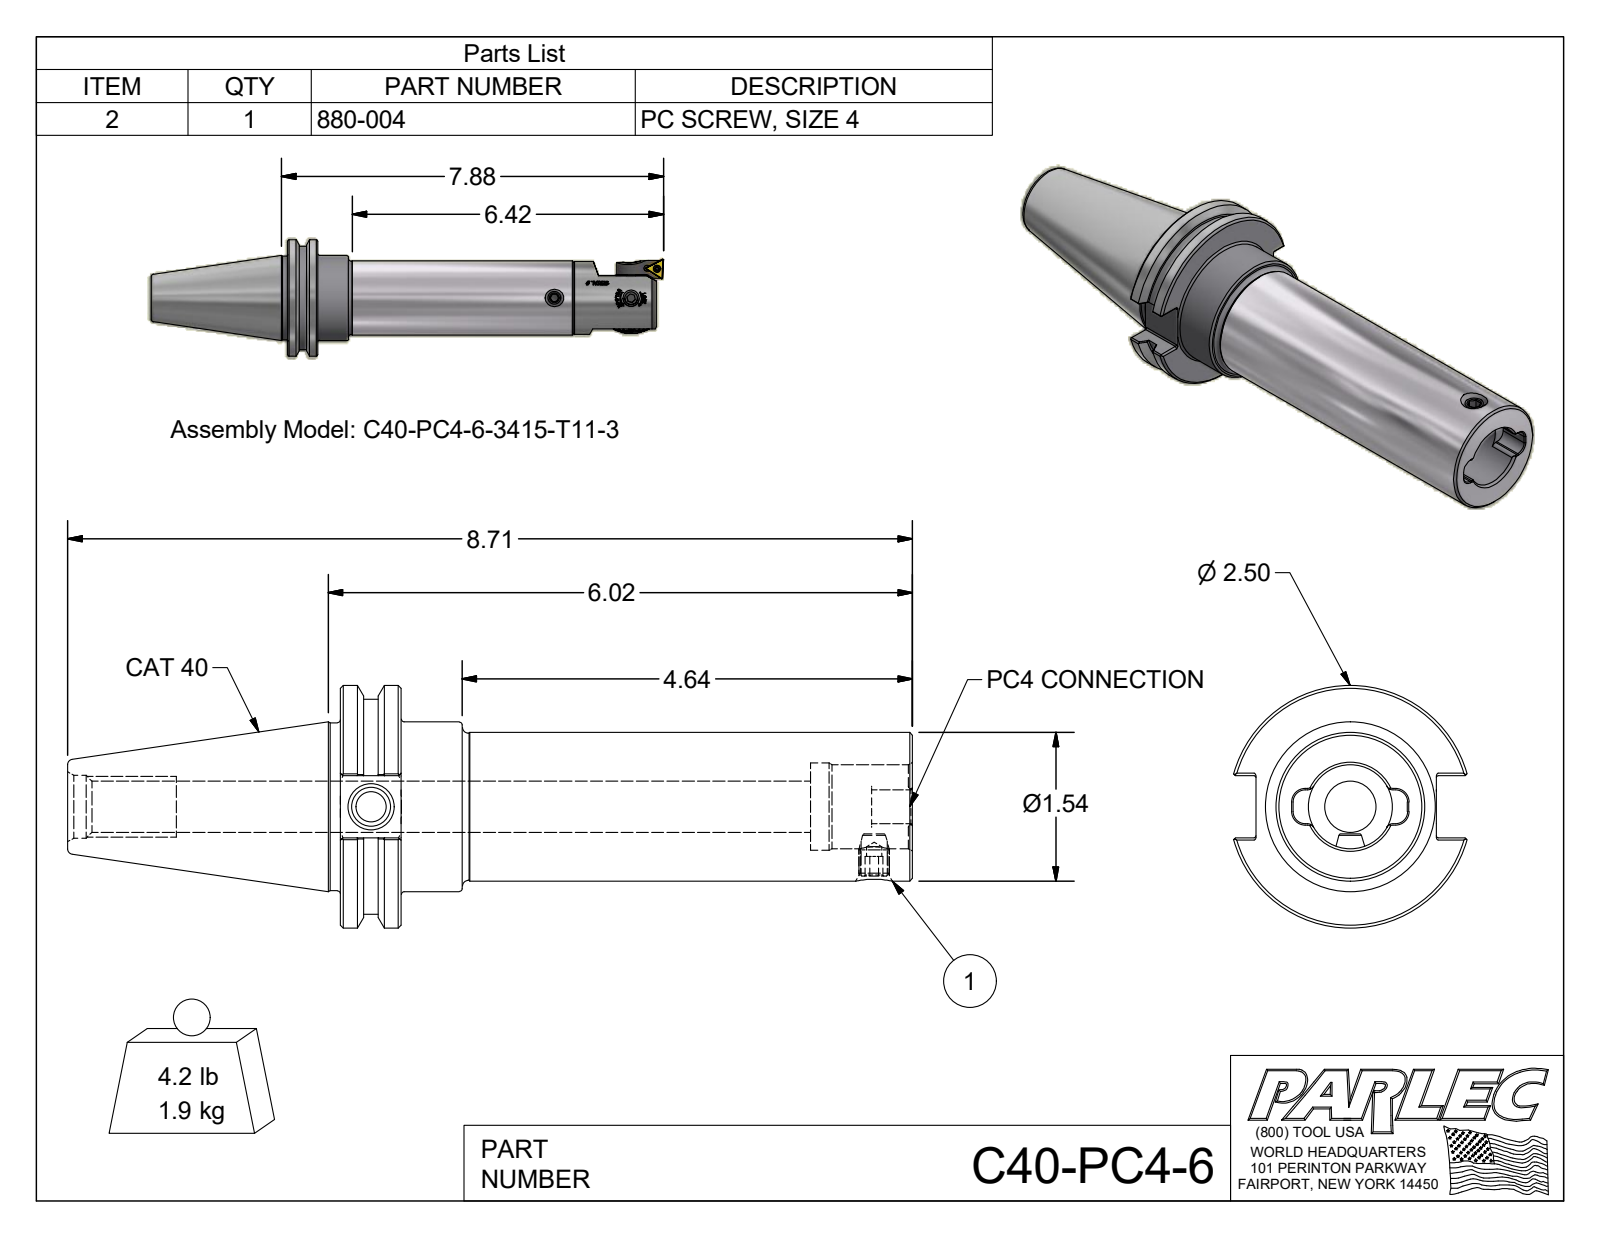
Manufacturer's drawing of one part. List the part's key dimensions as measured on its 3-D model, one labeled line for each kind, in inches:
Part name (STEP PRODUCT): C40-PC4-6; C40-PC4-6-1; 880-004
STEP written by: Autodesk Inventor 2018 (AUTOMOTIVE_DESIGN)
Units: inches
Bodies: 2 solids, 146 faces (61 planar, 39 cylindrical, 46 other)
Overall size (bounding box): 8.711 × 2.5 × 2.406
Volume: 14.64 in³ · Surface area: 67.77 in²
Round holes (diameter × count): ⌀0.158 ×1, ⌀0.283 ×1, ⌀0.315 ×1, ⌀0.399 ×1, ⌀0.527 ×1, ⌀0.648 ×1, ⌀0.866 ×1, ⌀0.9 ×1
Round bosses / shafts (diameter × count): ⌀2.5 ×1, ⌀2.219 ×1, ⌀1.75 ×1, ⌀1.73 ×1, ⌀1.535 ×1, ⌀1.515 ×1, ⌀0.315 ×1
Partial cylindrical surfaces — rounded edges, fillets, slot ends (radius × count): R0.02 ×12, R0.072 ×4, R0.125 ×4
Main face-to-face distances: 0.625, 5.899, 5.274, 1.051, 4.848, 4.223, 0.64, 1.86, 2.812, 3.437
